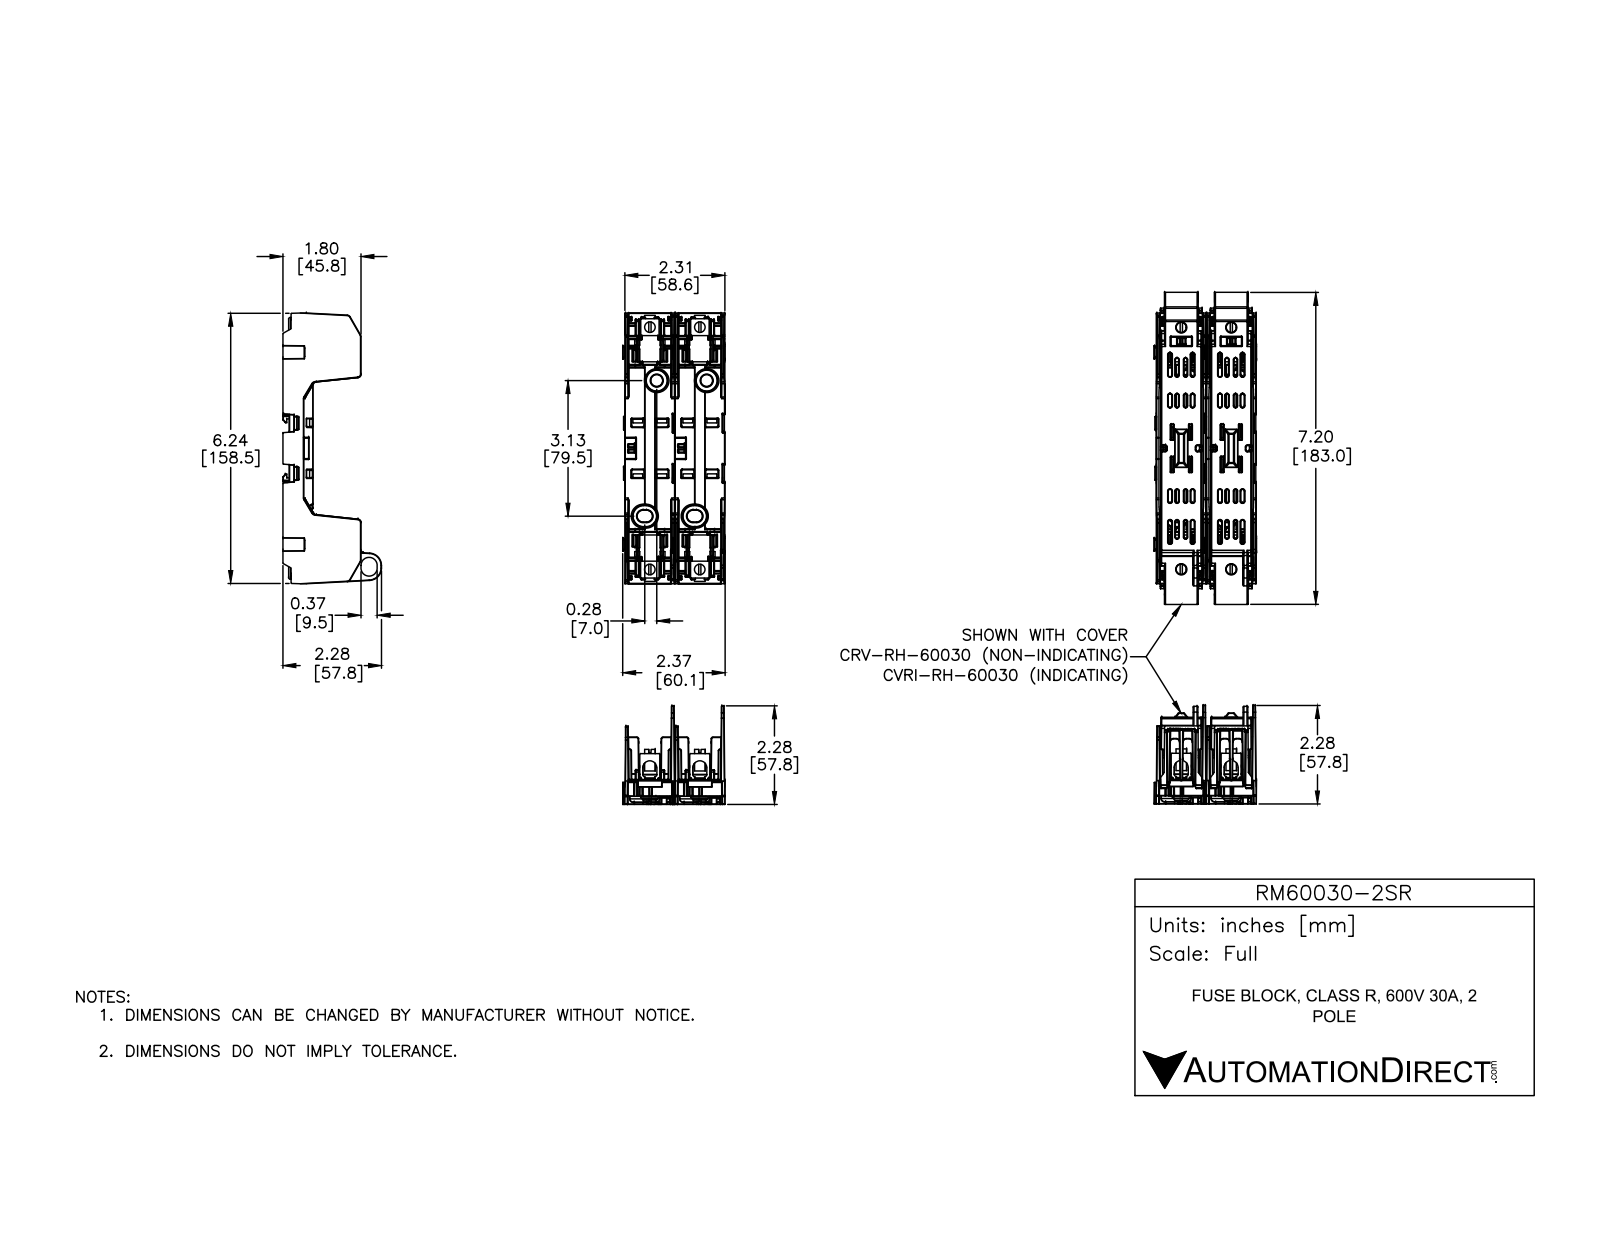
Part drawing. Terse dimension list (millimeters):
name: RM60030-2SR; RM60030-1SR
written by: SolidWorks 2018 (AUTOMOTIVE_DESIGN)
unit: mm
bodies: 14 solids, 7030 faces (1580 planar, 2946 cylindrical, 2504 other)
size: 158.9 × 60.2 × 57.8
volume: 104 300 mm³; area: 82 840 mm²
holes: 4× ⌀6.2
bosses: 4× ⌀6.2
rounds: 871× R0.3, 653× R0.2, 114× R0.5, 86× R1, 33× R2, 32× R0.5, 18× R1.9, 12× R1.5
face distances: 29.4, 27.1, 56.5, 2.3, 9.8, 4.7, 1.7, 15.5, 11.6, 12.4
hole spacings: 29.4, 142.2, 145.2, 145.2
